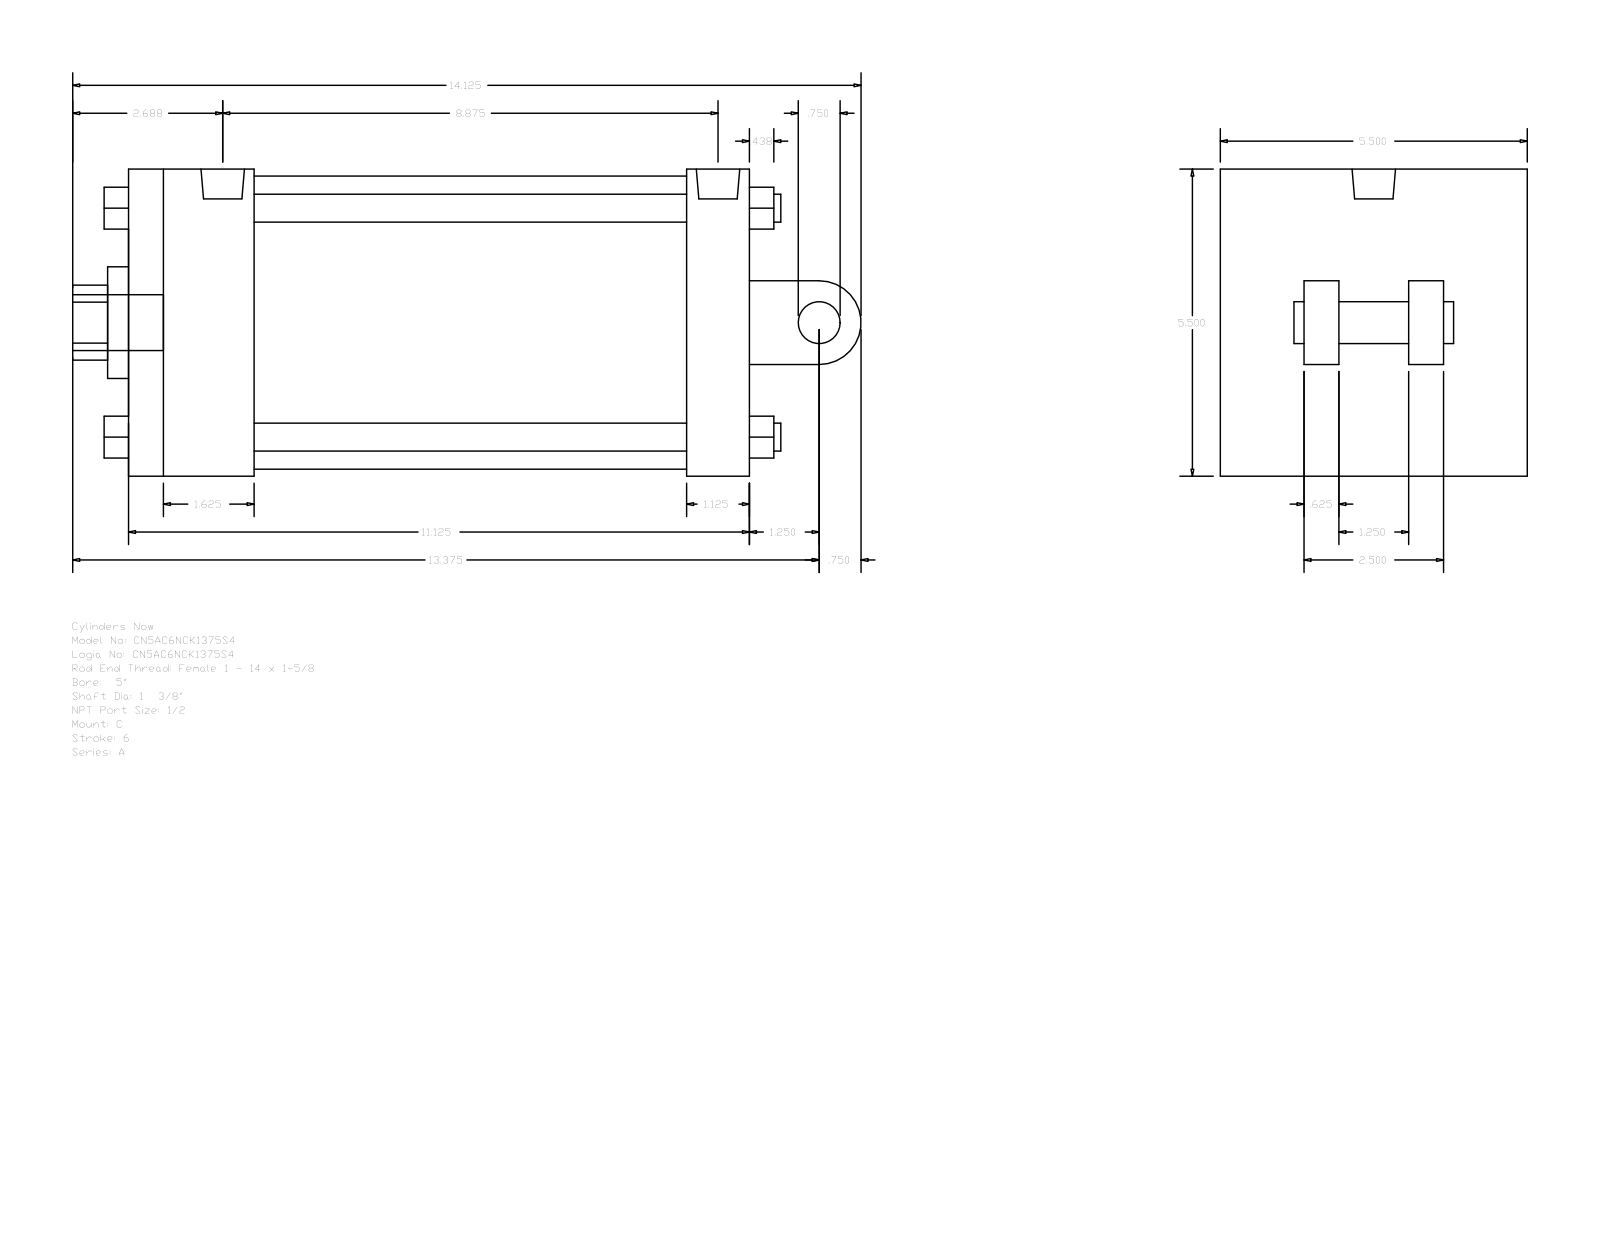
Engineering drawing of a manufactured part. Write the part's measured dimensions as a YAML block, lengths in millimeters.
part_name: "A_C__0500_1.375"
step_written_by: "GSSL Pune (CONFIG_CONTROL_DESIGN)"
units: millimeters
bodies: {solids: 0, faces: 135, planar: 102, cylindrical: 33, other: 0}
overall_size: [358.77, 139.7, 139.7]
round_holes:
  - {diameter: 8.73, count: 2}
  - {diameter: 19.77, count: 1}
  - {diameter: 34.92, count: 1}
  - {diameter: 50.8, count: 1}
  - {diameter: 133.35, count: 1}
round_bosses_or_shafts:
  - {diameter: 12.7, count: 4}
  - {diameter: 8.73, count: 2}
  - {diameter: 25.4, count: 1}
  - {diameter: 19.77, count: 1}
  - {diameter: 19.05, count: 1}
partial_cylinders:
  - {radius: 17.06, count: 1}
  - {radius: 19.05, count: 1}
face_to_face_distances: [139.7, 282.58, 28.58, 57.15, 254, 196.85, 225.43, 38.1, 15.87, 101.6]
hole_center_spacings: [2.39]
